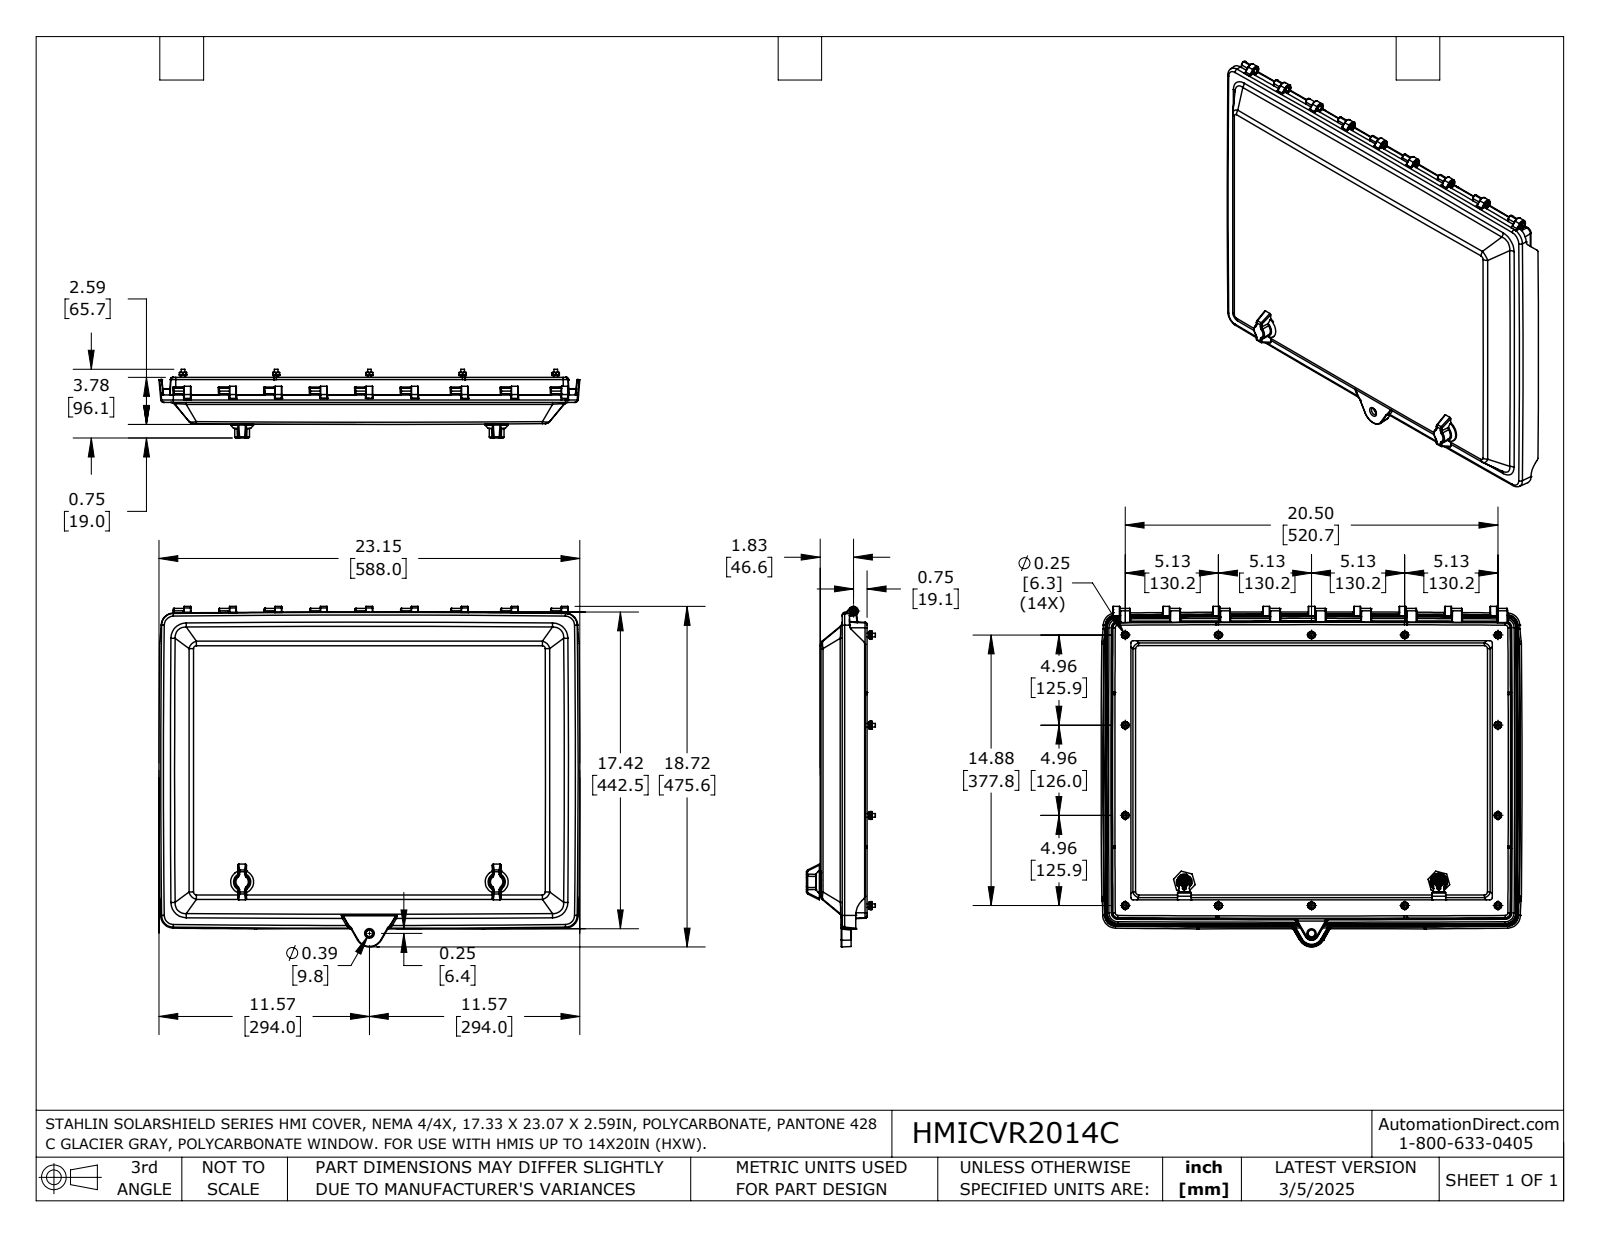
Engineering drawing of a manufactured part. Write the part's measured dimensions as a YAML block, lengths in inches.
part_name: "HMICVR2014C"
step_written_by: "SolidWorks 2024 (AUTOMOTIVE_DESIGN)"
units: inches
bodies: {solids: 71, faces: 2907, planar: 971, cylindrical: 709, other: 1227}
overall_size: [23.148, 18.724, 3.783]
volume: 100.1
surface_area: 1503
round_holes:
  - {diameter: 0.197, count: 16}
  - {diameter: 0.19, count: 14}
  - {diameter: 0.25, count: 14}
  - {diameter: 0.168, count: 2}
  - {diameter: 0.236, count: 2}
  - {diameter: 0.315, count: 2}
  - {diameter: 0.591, count: 2}
  - {diameter: 0.802, count: 2}
  - {diameter: 0.846, count: 2}
  - {diameter: 0.083, count: 1}
  - {diameter: 0.201, count: 1}
  - {diameter: 0.328, count: 1}
round_bosses_or_shafts:
  - {diameter: 0.394, count: 14}
  - {diameter: 0.373, count: 14}
  - {diameter: 0.199, count: 14}
  - {diameter: 1.26, count: 2}
  - {diameter: 0.78, count: 2}
  - {diameter: 0.531, count: 2}
  - {diameter: 0.217, count: 2}
  - {diameter: 0.189, count: 2}
partial_cylinders:
  - {radius: 0.02, count: 135}
  - {radius: 0.03, count: 76}
  - {radius: 0.012, count: 60}
  - {radius: 0.02, count: 32}
  - {radius: 0.04, count: 28}
  - {radius: 0.059, count: 12}
  - {radius: 0.106, count: 8}
  - {radius: 0.177, count: 6}
face_to_face_distances: [0.25, 1, 1.25, 1.125, 1.375, 0.125, 1.23, 0.98, 0.02, 0.145]
hole_center_spacings: [15.733, 18.065, 10.25, 14.875, 4.957, 5.125, 5.125, 9.917]
